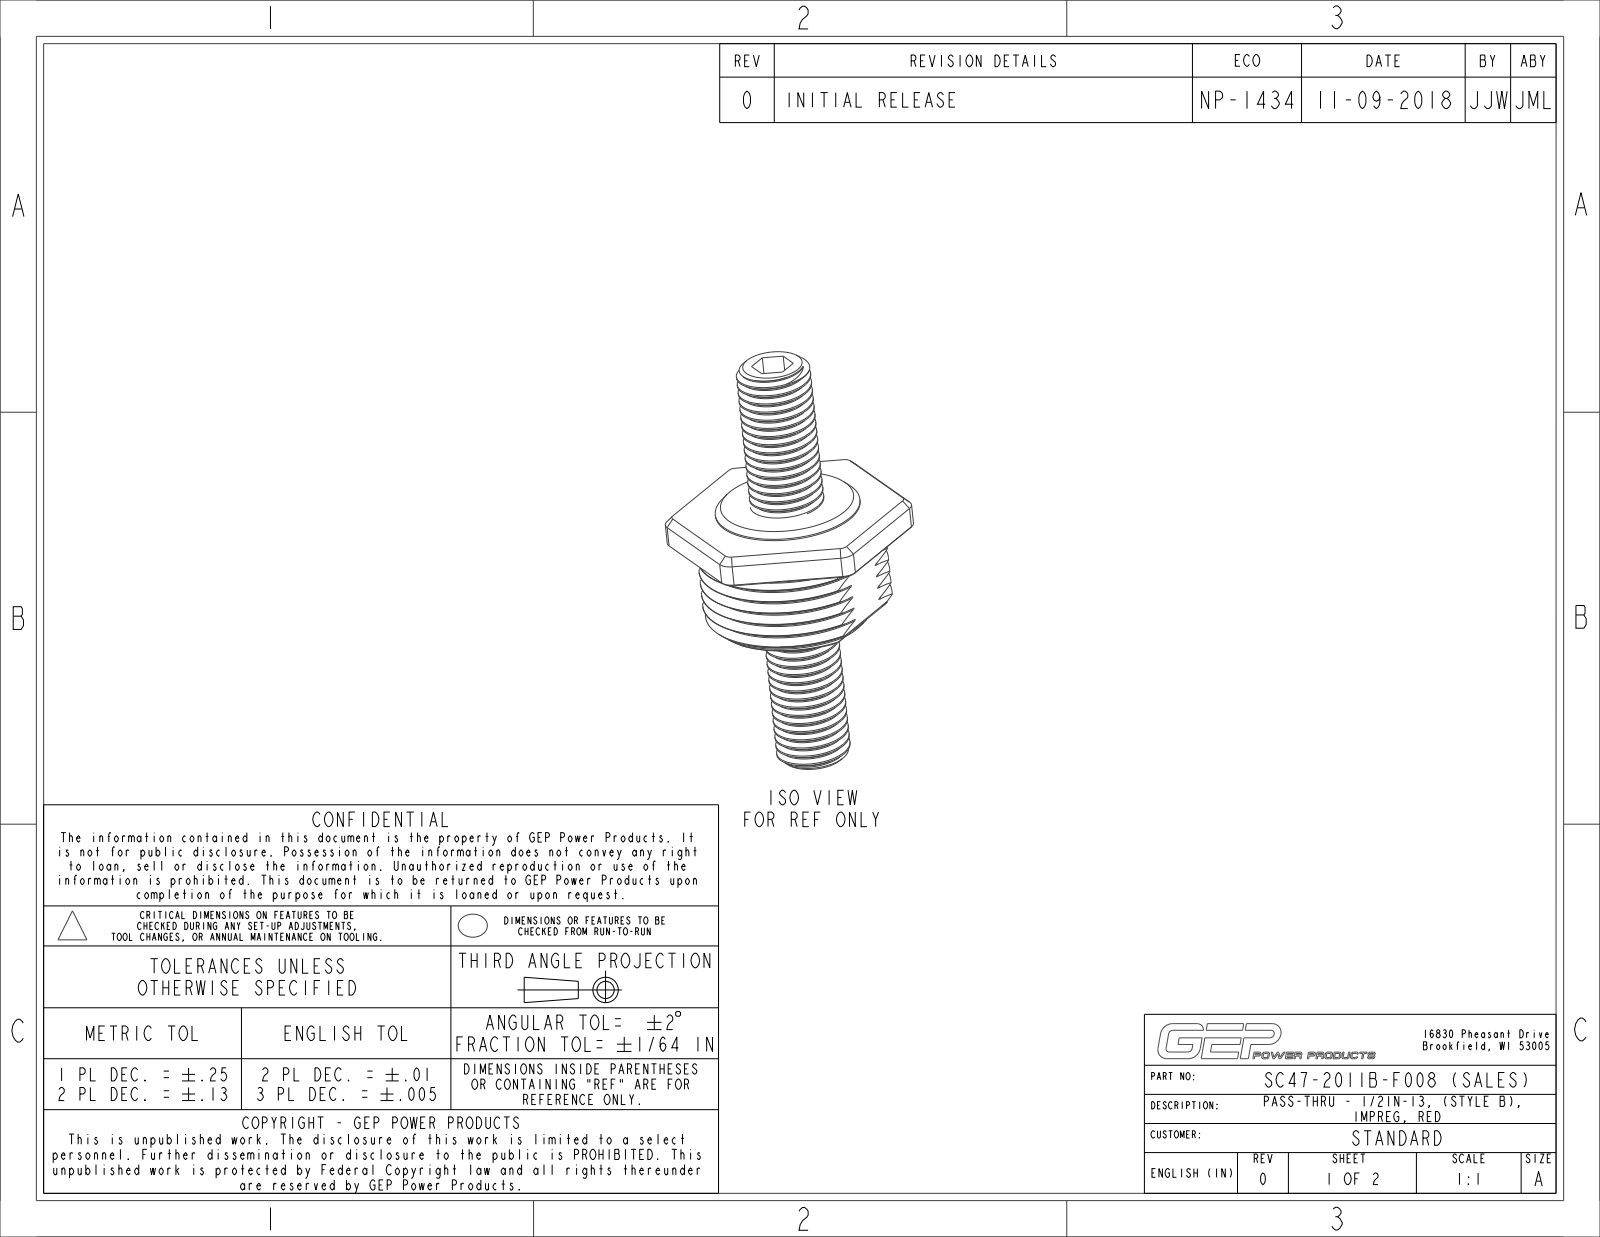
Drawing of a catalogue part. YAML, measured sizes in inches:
part_name: "SC47-2011B-F008_NCF_SW0001"
step_written_by: "CREO PARAMETRIC BY PTC INC, 2017110 (CONFIG_CONTROL_DESIGN)"
units: inches
bodies: {solids: 1, faces: 289, planar: 43, cylindrical: 106, other: 140}
overall_size: [3, 1.701, 1.5]
volume: 1.48
surface_area: 15.28
round_holes:
  - {diameter: 0.422, count: 1}
round_bosses_or_shafts:
  - {diameter: 1, count: 1}
  - {diameter: 0.51, count: 1}
partial_cylinders:
  - {radius: 0.1, count: 6}
  - {radius: 0.181, count: 6}
  - {radius: 0.03, count: 2}
  - {radius: 0.652, count: 1}
face_to_face_distances: [0.05, 0.85, 0.25, 0.2, 0.65, 0.9, 0.875, 0.625, 0.6, 1.5]
